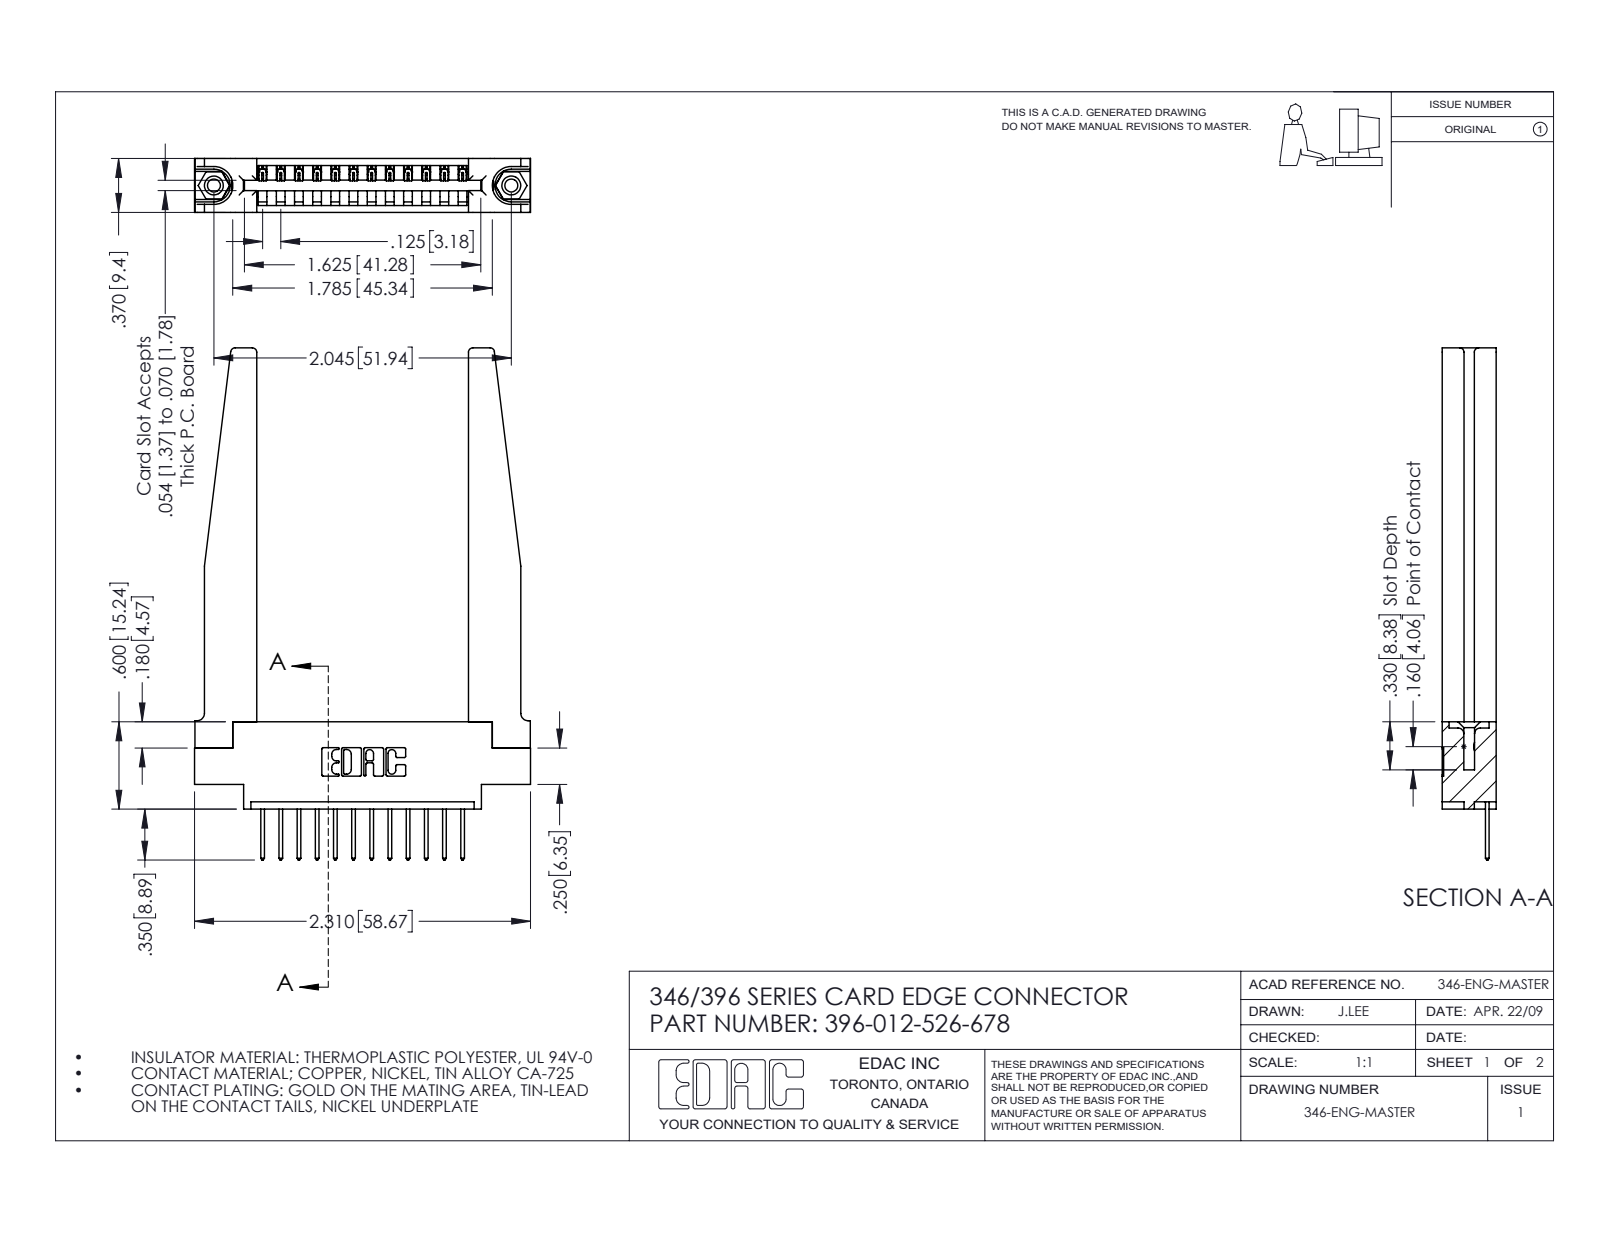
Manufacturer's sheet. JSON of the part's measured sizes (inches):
{"part_name": "346-220-078_345-220-078; 345-292-001_345-293-126; 346 Part_0.170 Offset - 0.156 Dia-TH; 396-012-526-678 (+1 more)", "step_written_by": "SolidWorks 2016 (CONFIG_CONTROL_DESIGN)", "units": "inches", "bodies": {"solids": 17, "faces": 1056, "planar": 702, "cylindrical": 302, "other": 52}, "overall_size": [3.52, 2.31, 0.37], "volume_in3": 0.742, "surface_area_in2": 20.03, "round_holes": [[0.089, 2], [0.125, 2], [0.156, 2], [0.064, 1]], "round_bosses_or_shafts": [[0.155, 2]], "partial_cylinders_radius": [[0.006, 24], [0.01, 24], [0.01, 22], [0.03, 8], [0.007, 6], [0.031, 6], [0.026, 3], [0.031, 2]], "face_to_face_distances": [0.37, 0.15, 0.148, 0.072, 0.048, 0.322, 0.25, 0.22, 0.102, 0.173], "hole_center_spacings": [0.246, 1.839, 2.045]}
